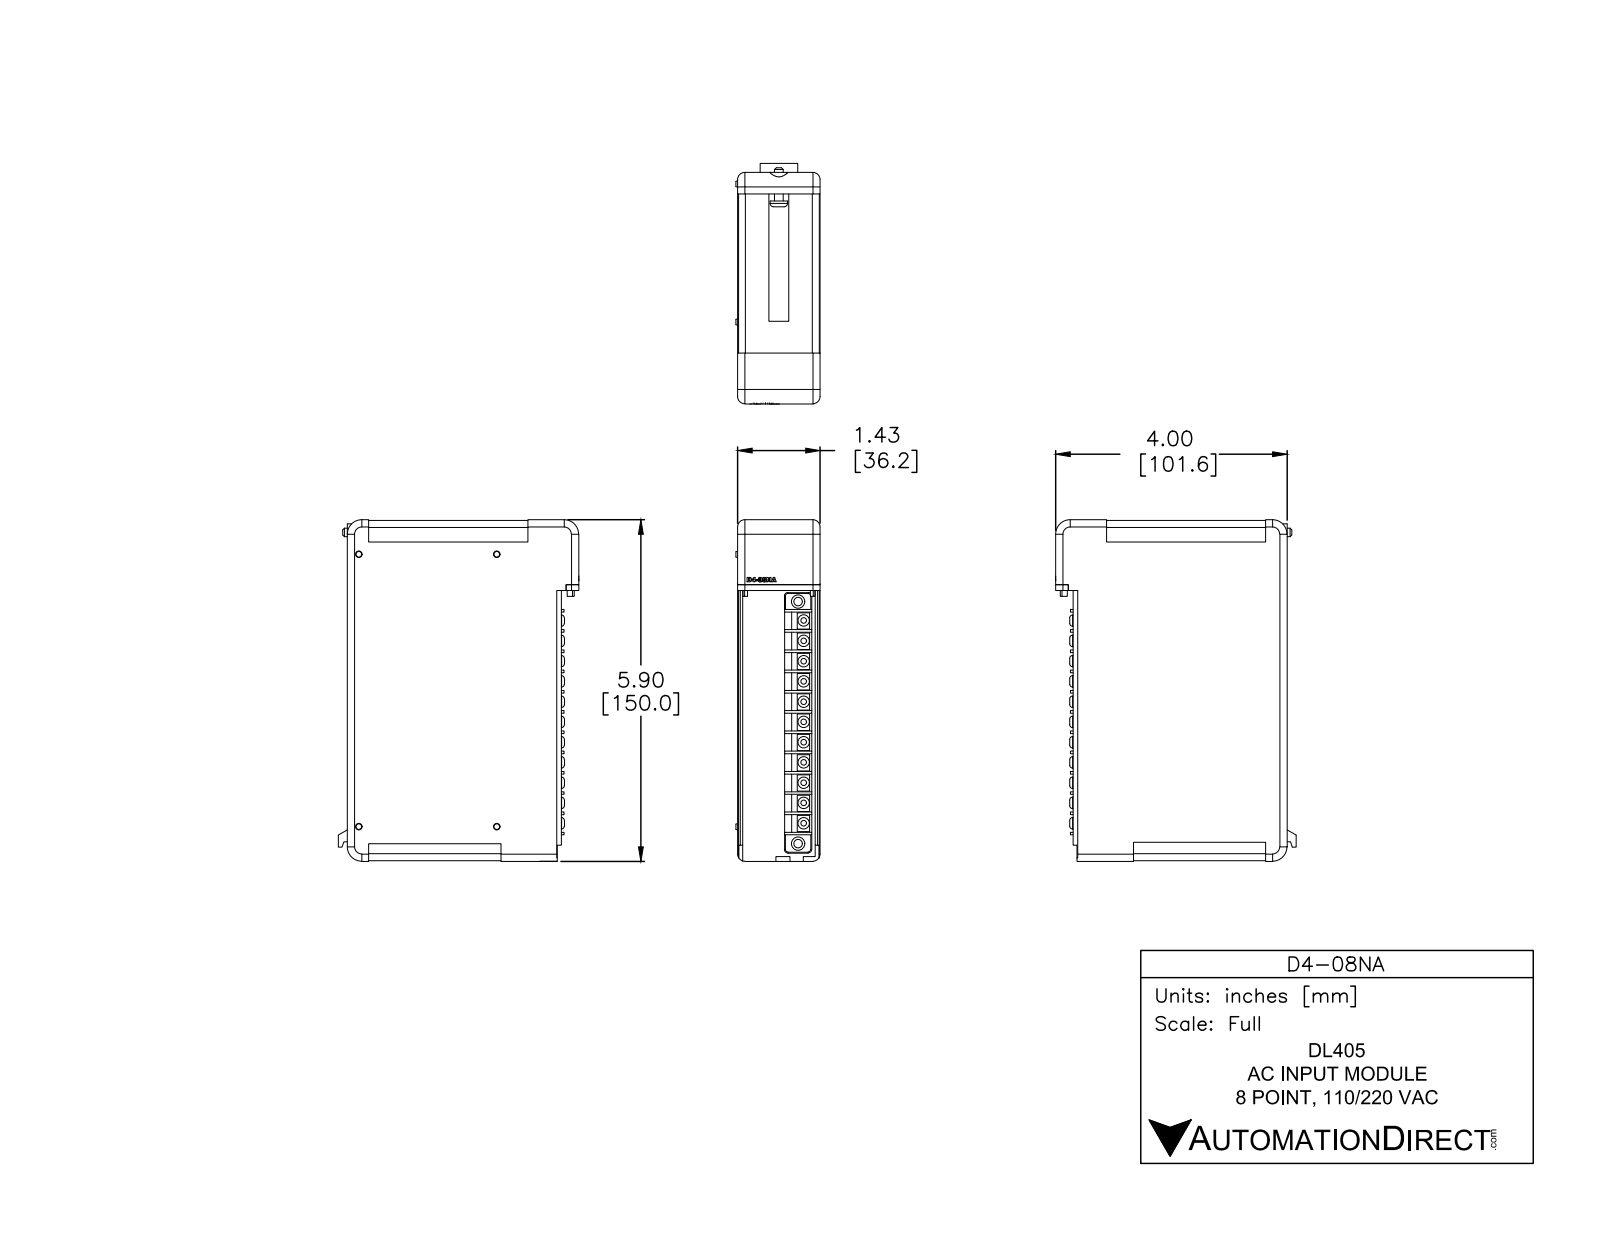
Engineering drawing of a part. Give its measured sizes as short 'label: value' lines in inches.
name: D4-08NA
written by: SolidWorks 2014 (AUTOMOTIVE_DESIGN)
unit: in
bodies: 10 solids, 445 faces (292 planar, 71 cylindrical, 82 other)
size: 5.905 × 4.156 × 1.455
volume: 29.11 in³; area: 85.82 in²
bosses: 11× ⌀0.2, 2× ⌀0.229, 1× ⌀0.3, 1× ⌀0.15
rounds: 8× R0.125, 6× R0.015, 4× R0.06, 4× R0.12, 3× R0.25, 2× R0.03, 1× R0.151, 1× R0.171
face distances: 1.425, 0.015, 3.325, 0.085, 1.34, 5.875, 0.07, 0.2, 1.41, 1.325
